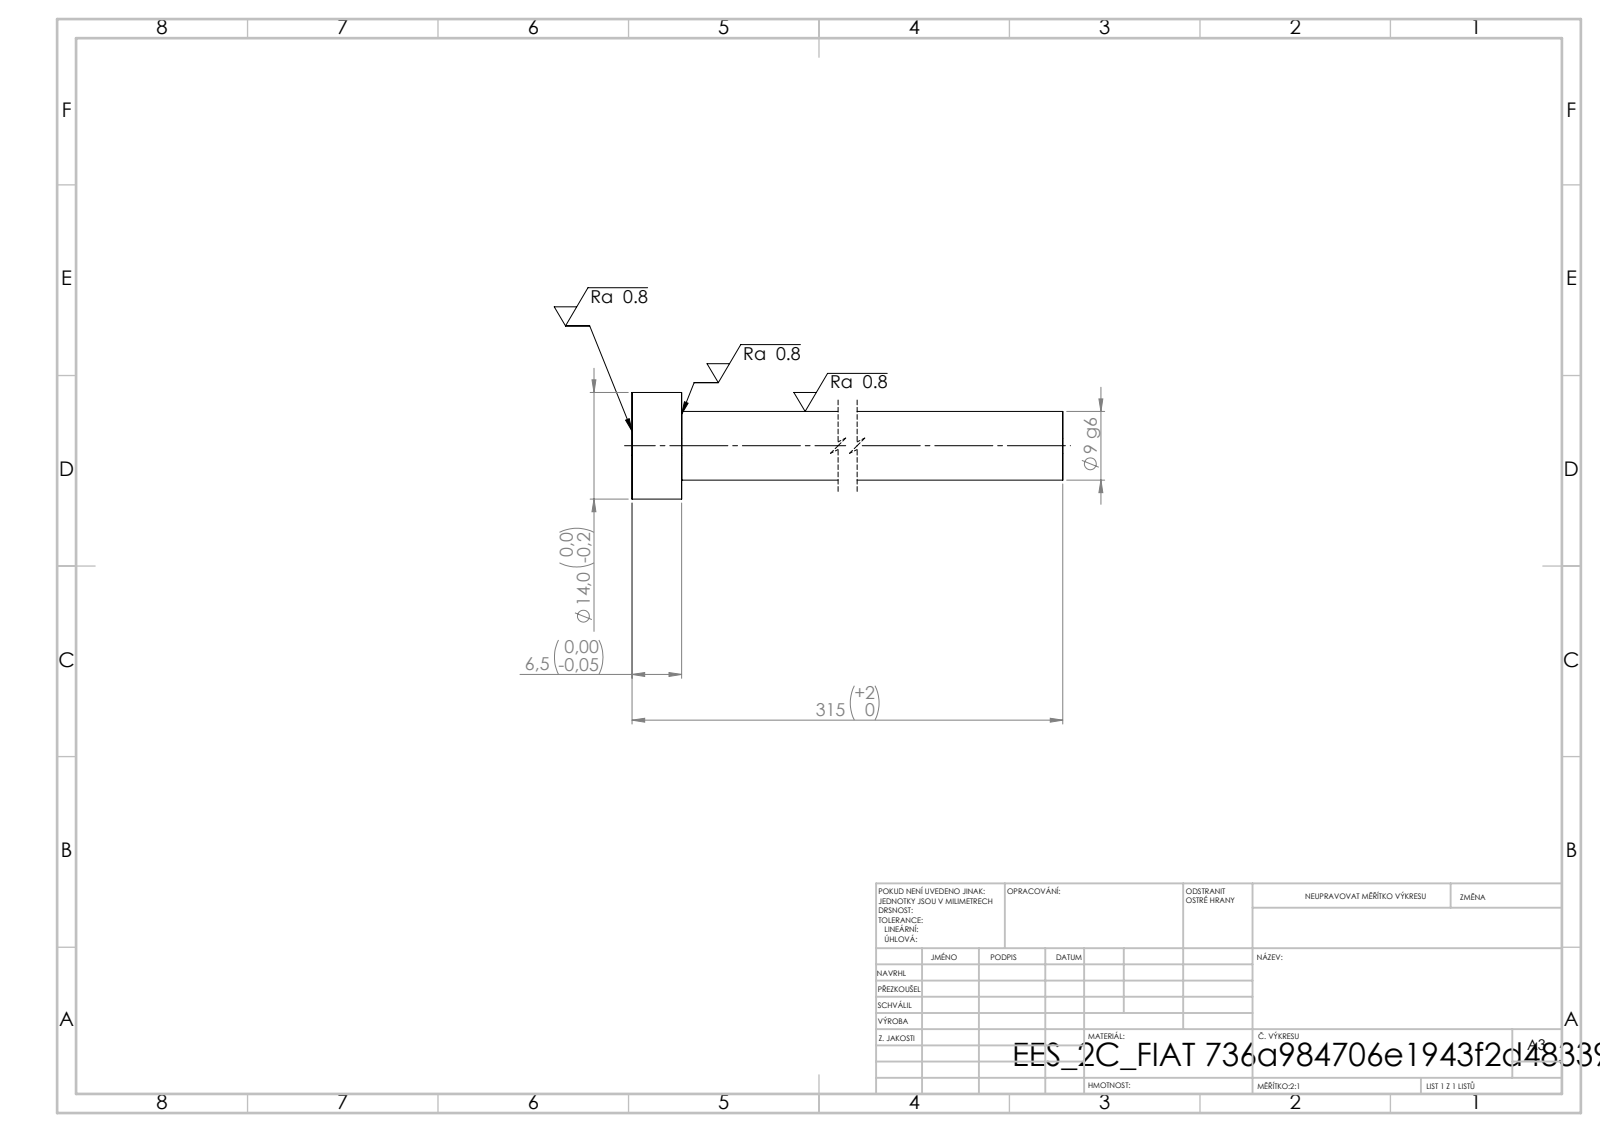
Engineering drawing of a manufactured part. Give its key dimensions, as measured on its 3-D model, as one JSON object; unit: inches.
{"step_written_by": "SolidWorks 2019 (CONFIG_CONTROL_DESIGN)", "units": "inches", "bodies": {"solids": 1, "faces": 7, "planar": 3, "cylindrical": 4, "other": 0}, "overall_size": [12.402, 0.551, 0.551], "volume_in3": 1.259, "surface_area_in2": 14.44, "round_bosses_or_shafts": [[0.551, 1], [0.354, 1]], "face_to_face_distances": [0.256, 12.402, 12.146]}
